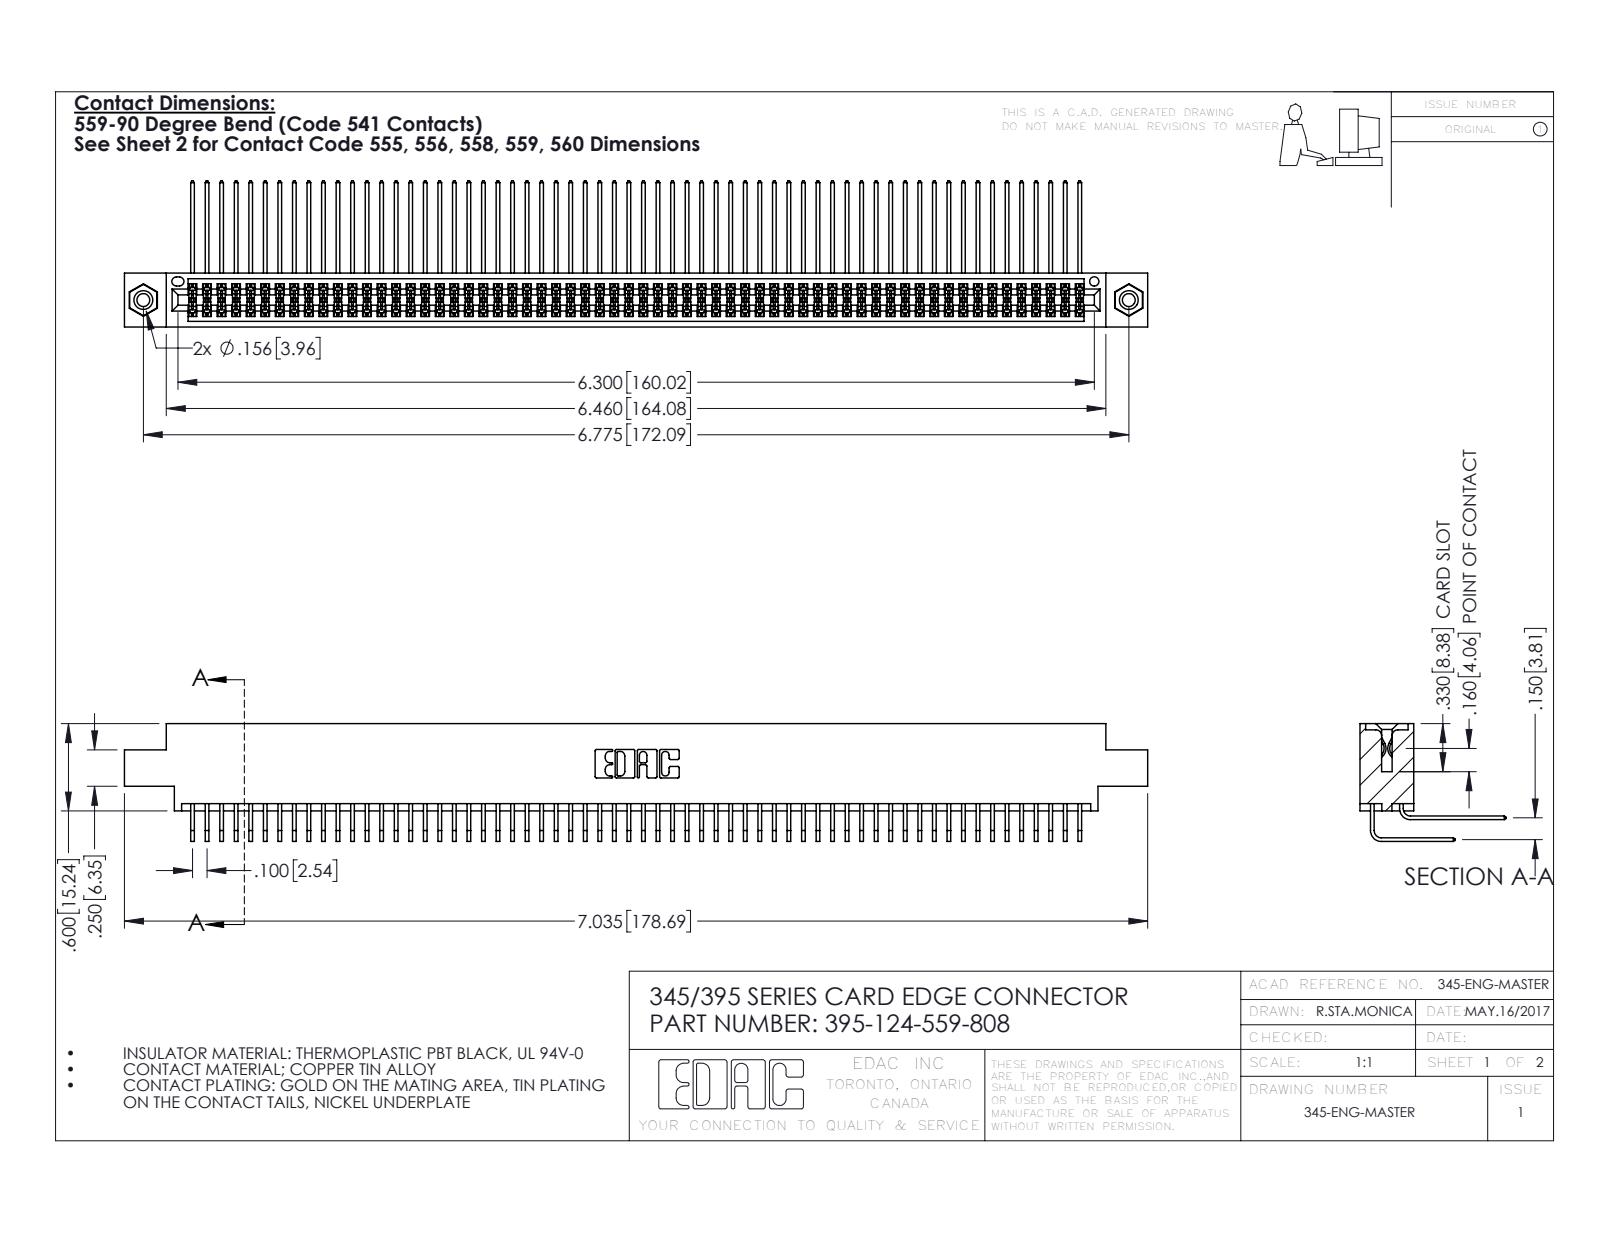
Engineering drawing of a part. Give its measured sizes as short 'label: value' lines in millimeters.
name: 345-292-001_558 559 Tail - 1; 345-250-001_345-250-003-102; 395-124-559-808; 345-292-001_559 Tail - 2 (+1 more)
written by: SolidWorks 2016 (CONFIG_CONTROL_DESIGN)
unit: mm
bodies: 127 solids, 6638 faces (4456 planar, 2166 cylindrical, 16 other)
size: 178.7 × 25.5 × 20.5
volume: 18 140 mm³; area: 30 720 mm²
holes: 2× ⌀2.3, 2× ⌀3.2, 2× ⌀4, 1× ⌀1.6
bosses: 2× ⌀3.9
rounds: 186× R0.2, 22× R0.3, 6× R0.2, 6× R0.8, 3× R0.7, 2× R0.4, 2× R0.5, 2× R0.6
face distances: 1.8, 7.6, 9.4, 5.1, 2.5, 6.9, 0.6, 5.7, 4.4, 3.8
hole spacings: 6.9, 166.1, 172.1
